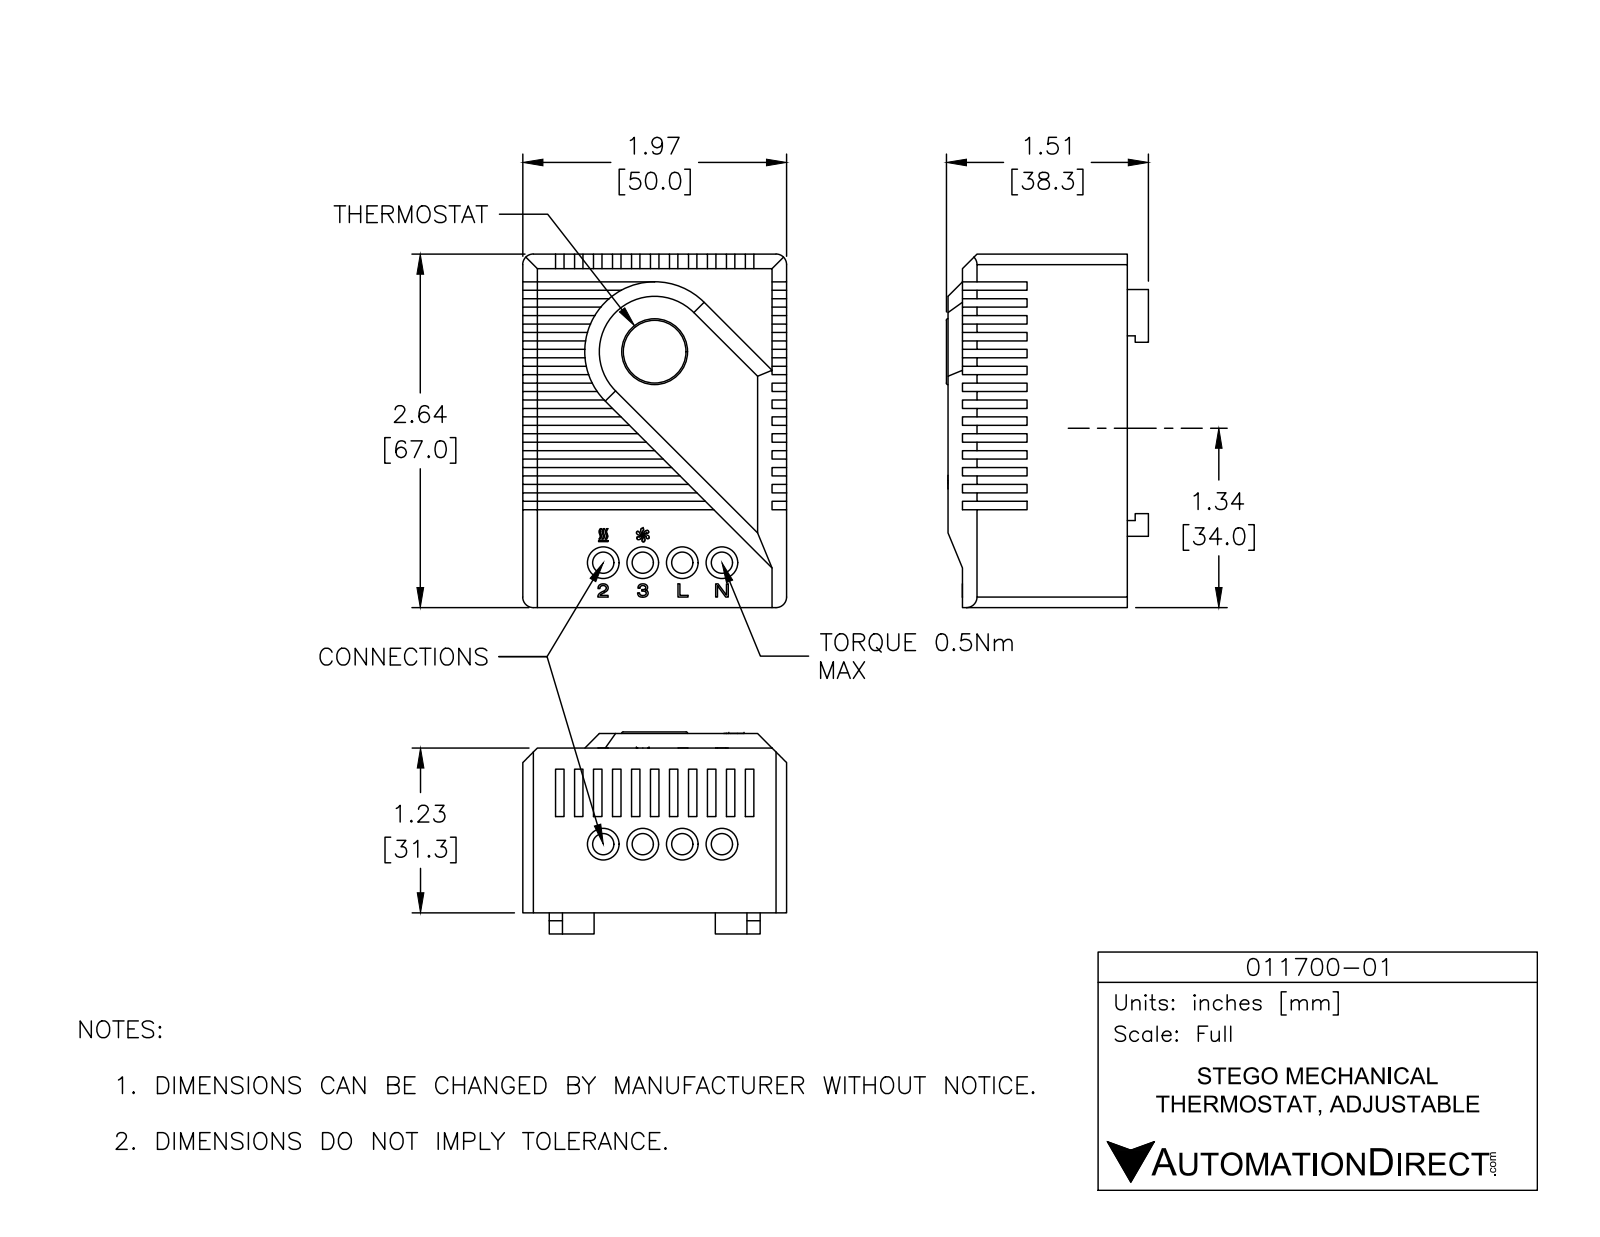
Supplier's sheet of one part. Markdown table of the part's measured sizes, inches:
| quantity | value |
| --- | --- |
| part name | 011700-00 |
| STEP written by | SolidWorks 2017 (AUTOMOTIVE_DESIGN) |
| units | inches |
| bodies | 1 solid, 610 faces (385 planar, 44 cylindrical, 181 other) |
| overall size | 2.638 × 1.969 × 1.508 |
| volume | 6.324 in³ |
| surface area | 28.57 in² |
| round holes (diameter × count) | 0.157 × 8, 0.236 × 8 |
| partial cylindrical surfaces (radius × count) | 0.079 × 4, 0.522 × 1 |
| main face-to-face distances | 0.063, 1.969, 0.108, 1.23, 0.126, 2.638, 0.189, 0.252, 0.079, 0.315 |
| hole center spacings | 0.295, 0.591, 0.886 |
